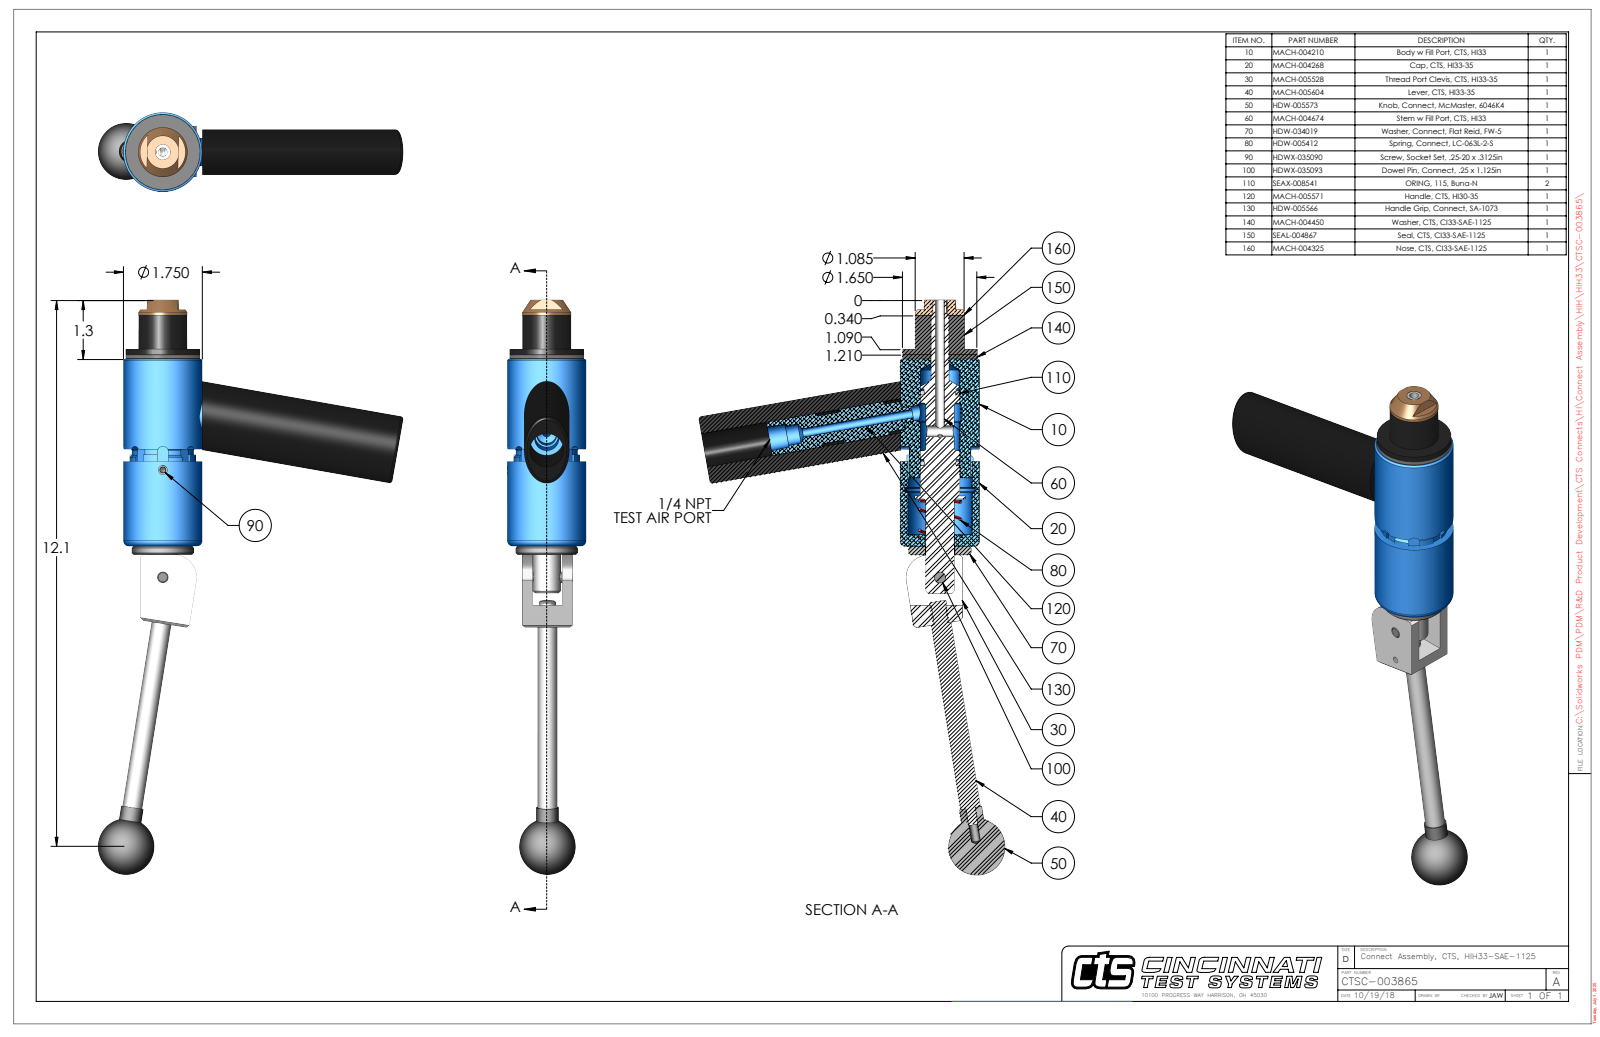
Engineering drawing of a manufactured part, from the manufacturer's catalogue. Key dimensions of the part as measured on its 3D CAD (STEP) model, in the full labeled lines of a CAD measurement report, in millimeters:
Part name (STEP PRODUCT): CTSC-003865
STEP written by: SolidWorks 2023 (AUTOMOTIVE_DESIGN)
Units: millimetres
Bodies: 10 solids, 327 faces (117 planar, 140 cylindrical, 70 other)
Overall size (bounding box): 323.3 × 171.8 × 44.5
Volume: 305 300 mm³ · Surface area: 76 190 mm²
Round holes (diameter × count): ⌀5.1 ×2, ⌀8 ×2, ⌀3.8 ×1, ⌀4.7 ×1, ⌀5.2 ×1, ⌀6.3 ×1, ⌀6.4 ×1, ⌀6.4 ×1, ⌀9.9 ×1, ⌀10.1 ×1, ⌀10.2 ×1, ⌀11.1 ×1
Round bosses / shafts (diameter × count): ⌀7.9 ×2, ⌀6.4 ×2, ⌀44.5 ×1, ⌀41.9 ×1, ⌀35.1 ×1, ⌀27.6 ×1, ⌀19.1 ×1, ⌀15.9 ×1
Partial cylindrical surfaces — rounded edges, fillets, slot ends (radius × count): R3.2 ×4, R0.7 ×2, R3.8 ×1, R4.2 ×1, R4.2 ×1, R8.4 ×1, R12.7 ×1, R17.7 ×1
Main face-to-face distances: 2.5, 107.8, 105.3, 22.1, 24.6, 129.9, 28.4, 134.7, 112.6, 110.1
Hole centre spacings: 18.8, 60.4, 79.1
